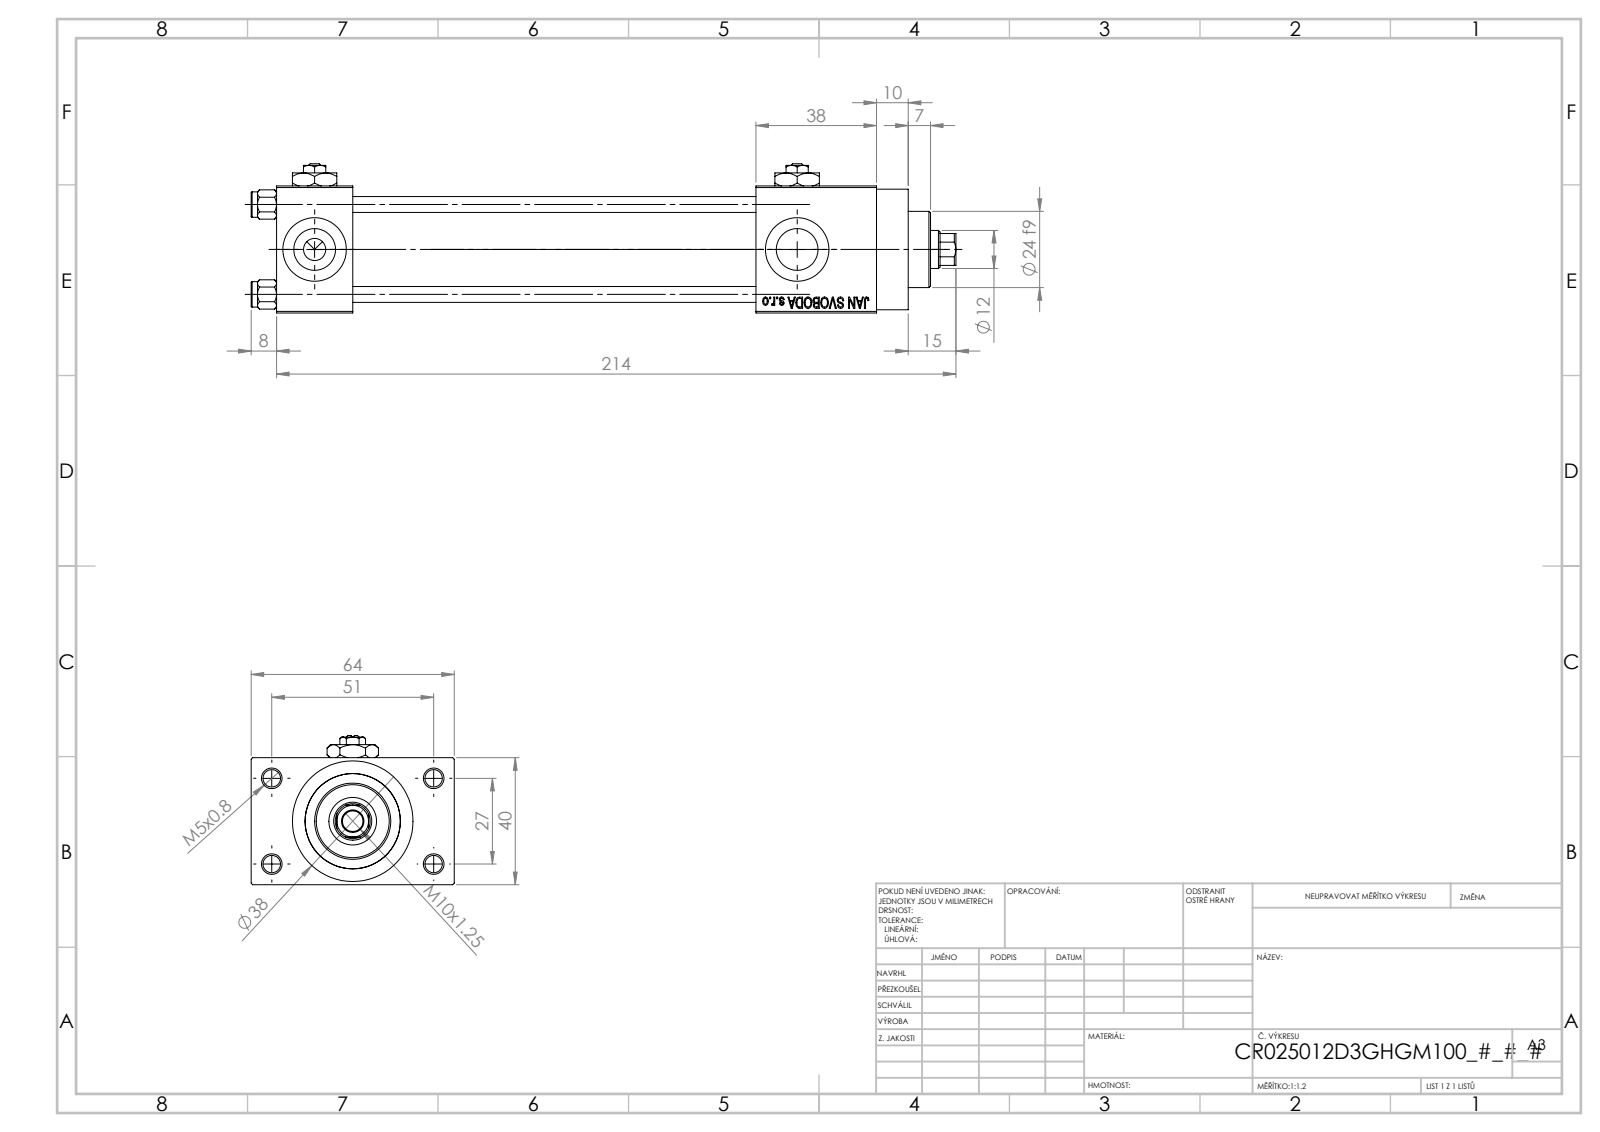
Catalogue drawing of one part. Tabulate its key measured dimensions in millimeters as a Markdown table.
| quantity | value |
| --- | --- |
| part name | V215_VC_A; V215CR_VCP_D; V215CR_D_Body; NUT_M5_D (+2 more) |
| STEP written by | SolidWorks 2019 (CONFIG_CONTROL_DESIGN) |
| units | millimeters |
| bodies | 13 solids, 1201 faces (542 planar, 99 cylindrical, 560 other) |
| overall size | 222 × 64 × 47 |
| volume | 209 101 mm³ |
| surface area | 85 923 mm² |
| round holes (diameter × count) | 20 × 5, 5 × 4, 5.5 × 4, 13.16 × 4, 7 × 3, 6.5 × 1, 12 × 1, 15 × 1, 25 × 1, 30 × 1 |
| round bosses / shafts (diameter × count) | 8 × 4, 38 × 1, 31 × 1, 24 × 1 |
| partial cylindrical surfaces (radius × count) | 5.5 × 1 |
| main face-to-face distances | 40, 12, 127, 24, 151, 52, 38, 165, 189, 64 |
| hole center spacings | 11.37, 20.01, 28.3, 28.85, 29.89, 39.66, 48.34, 27 |
